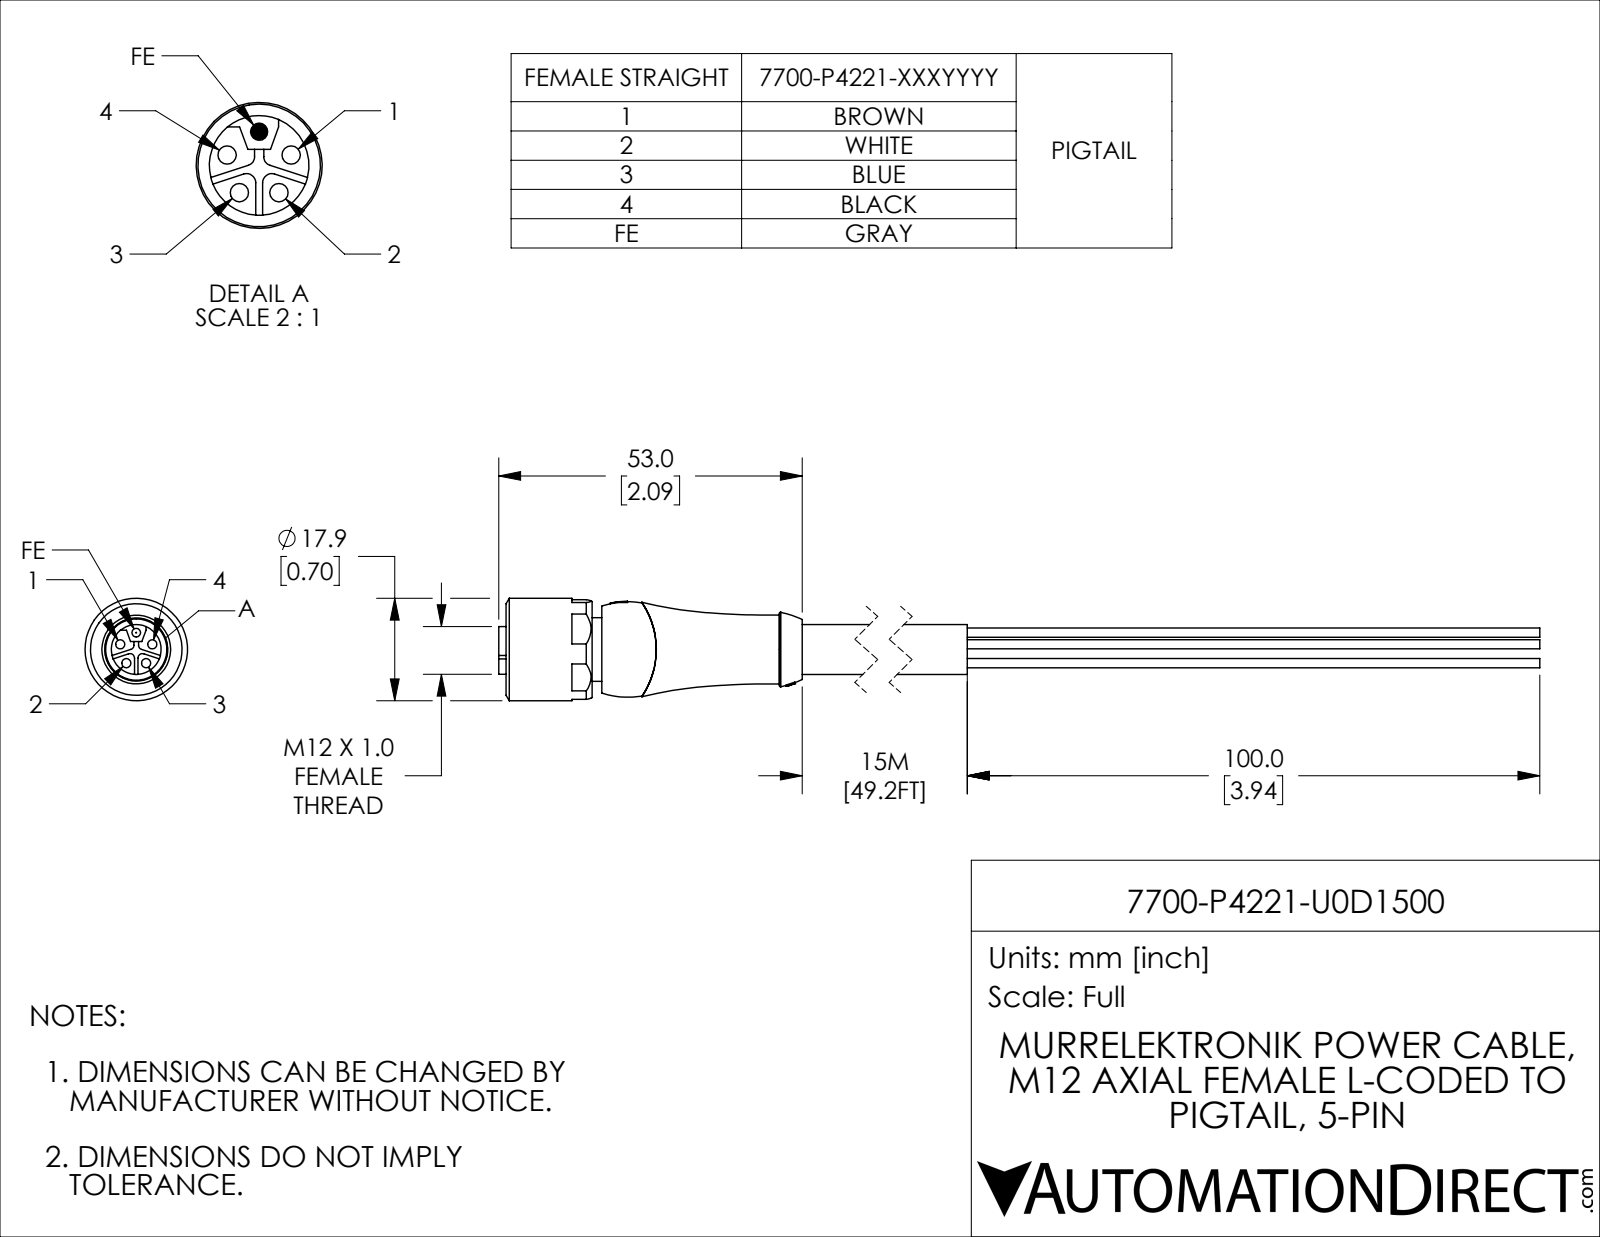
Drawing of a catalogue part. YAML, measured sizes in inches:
part_name: "7700-P4221-U0D1500"
step_written_by: "SolidWorks 2021 (CONFIG_CONTROL_DESIGN)"
units: inches
bodies: {solids: 2, faces: 142, planar: 69, cylindrical: 40, other: 33}
overall_size: [7.598, 0.705, 0.705]
volume: 0.735
surface_area: 12.83
round_holes:
  - {diameter: 0.063, count: 4}
  - {diameter: 0.433, count: 1}
  - {diameter: 0.512, count: 1}
round_bosses_or_shafts:
  - {diameter: 0.705, count: 1}
  - {diameter: 0.51, count: 1}
  - {diameter: 0.437, count: 1}
  - {diameter: 0.343, count: 1}
  - {diameter: 0.063, count: 1}
  - {diameter: 0.059, count: 1}
partial_cylinders:
  - {radius: 0.031, count: 4}
face_to_face_distances: [0.657, 0.591, 0.067, 0.667, 3.61, 3.02, 2.953, 0.181, 0.362, 0.228]
hole_center_spacings: [0.116, 0.136, 0.22]
